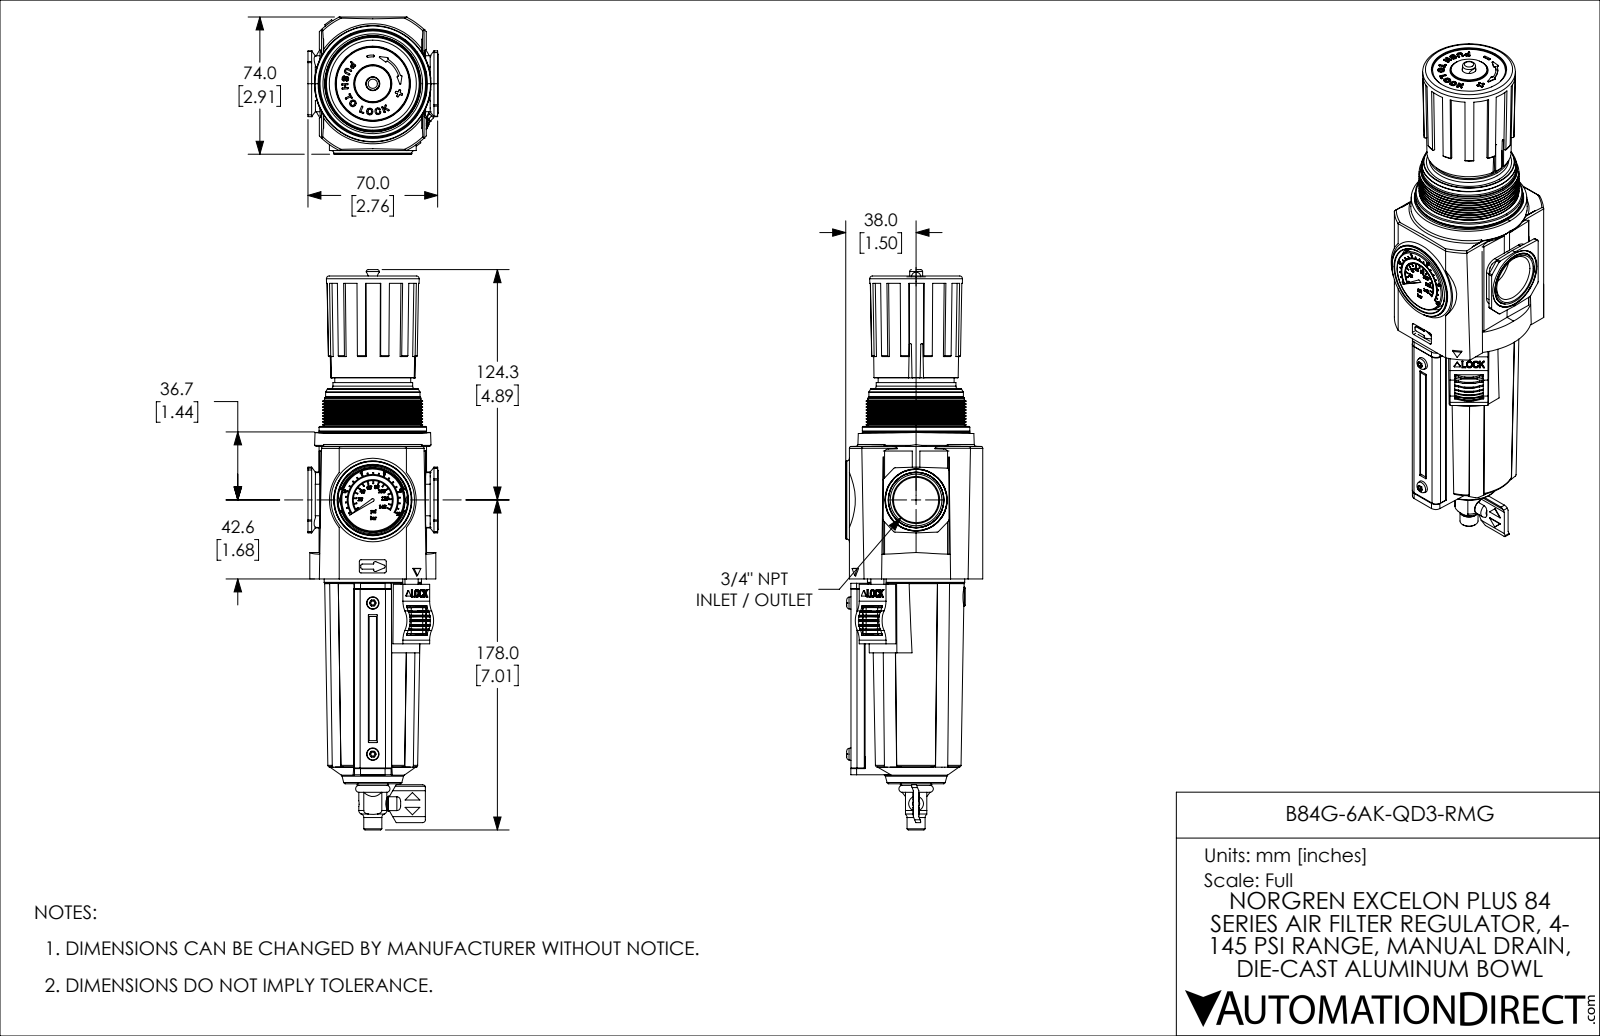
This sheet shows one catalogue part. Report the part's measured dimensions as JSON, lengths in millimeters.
{"part_name": "B84G-6AK-QD3-RMG", "step_written_by": "SolidWorks 2021 (CONFIG_CONTROL_DESIGN)", "units": "millimeters", "bodies": {"solids": 9, "faces": 2693, "planar": 980, "cylindrical": 1218, "other": 495}, "overall_size": [302.3, 74, 70.3], "volume_mm3": 755000, "surface_area_mm2": 146200, "round_holes": [[2.8, 2], [4.5, 2], [1.5, 1], [3.1, 1], [3.2, 1], [5, 1], [6, 1], [6.4, 1], [9.5, 1], [16.1, 1], [33.5, 1], [59, 1]], "round_bosses_or_shafts": [[7.6, 2], [5.4, 2], [4, 2], [58, 1], [53.9, 1], [53.8, 1], [52.5, 1], [52, 1]], "partial_cylinders_radius": [[1, 37], [0.7, 28], [0.3, 27], [0.5, 23], [0.3, 18], [1.2, 18], [0.8, 16], [0.1, 14]], "face_to_face_distances": [69.1, 59, 62.4, 9.2, 59.8, 15.8, 13, 3.4, 53.2, 44], "hole_center_spacings": [21.7, 68.2, 130.1, 43.5, 63.6, 64.6, 128.2, 284.2]}
